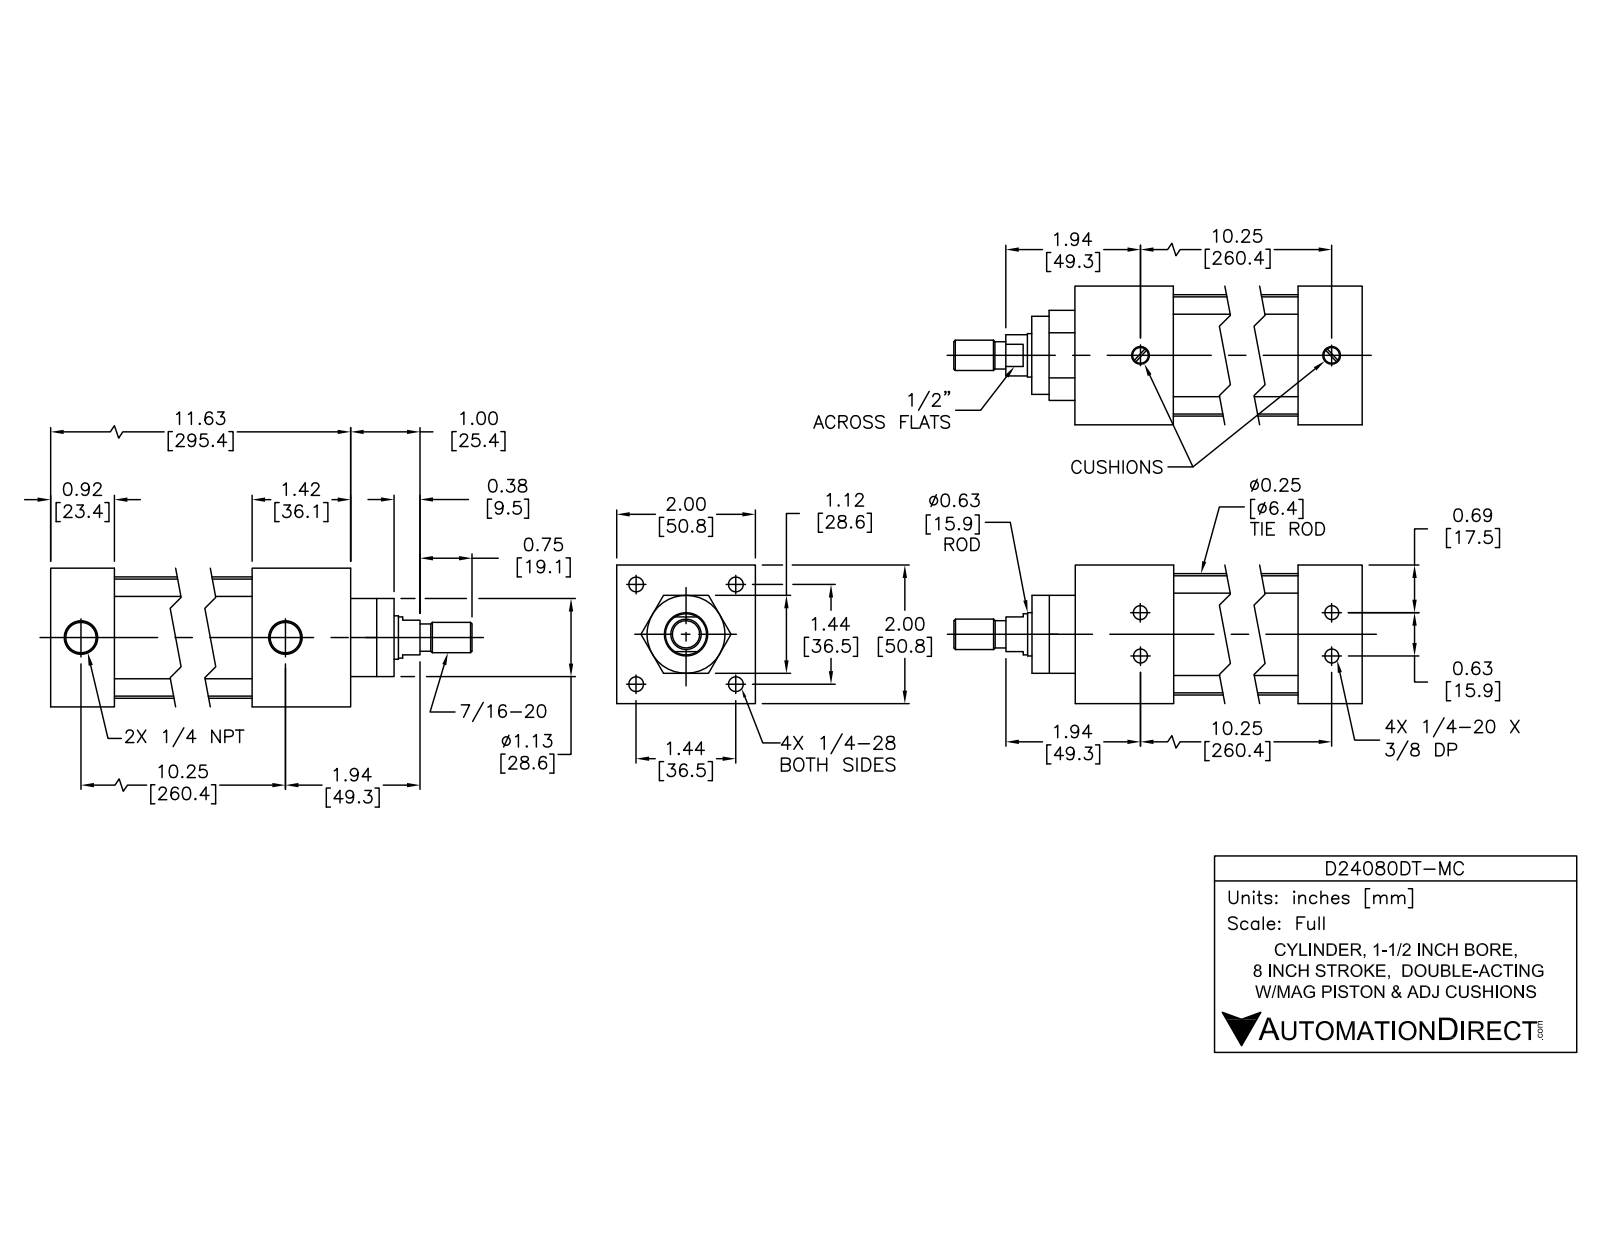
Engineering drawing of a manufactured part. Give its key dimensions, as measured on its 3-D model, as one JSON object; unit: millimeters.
{"part_name": "D24080DT-MC; D24080DT-M BODY; D24080DT-M PISTON", "step_written_by": "SolidWorks 2015 (AUTOMOTIVE_DESIGN)", "units": "millimeters", "bodies": {"solids": 12, "faces": 303, "planar": 99, "cylindrical": 114, "other": 90}, "overall_size": [339.6, 50.8, 50.8], "volume_mm3": 351700, "surface_area_mm2": 137200, "round_holes": [[5, 4], [5.4, 4], [7.1, 4], [10.3, 4], [7.5, 2], [12.1, 2], [15.9, 1], [16, 1], [38.1, 1]], "round_bosses_or_shafts": [[9.9, 4], [6.4, 4], [5.6, 4], [44.5, 1], [38, 1], [28.5, 1], [15.8, 1], [15, 1]], "partial_cylinders_radius": [[5.1, 4]], "face_to_face_distances": [50.8, 2, 233.7, 295.2, 36.1, 259.1, 271.8, 235.7, 23.4, 28.5], "hole_center_spacings": [36.4, 260.4, 7.9, 8, 15.9, 25.8, 51.5, 260.3]}
